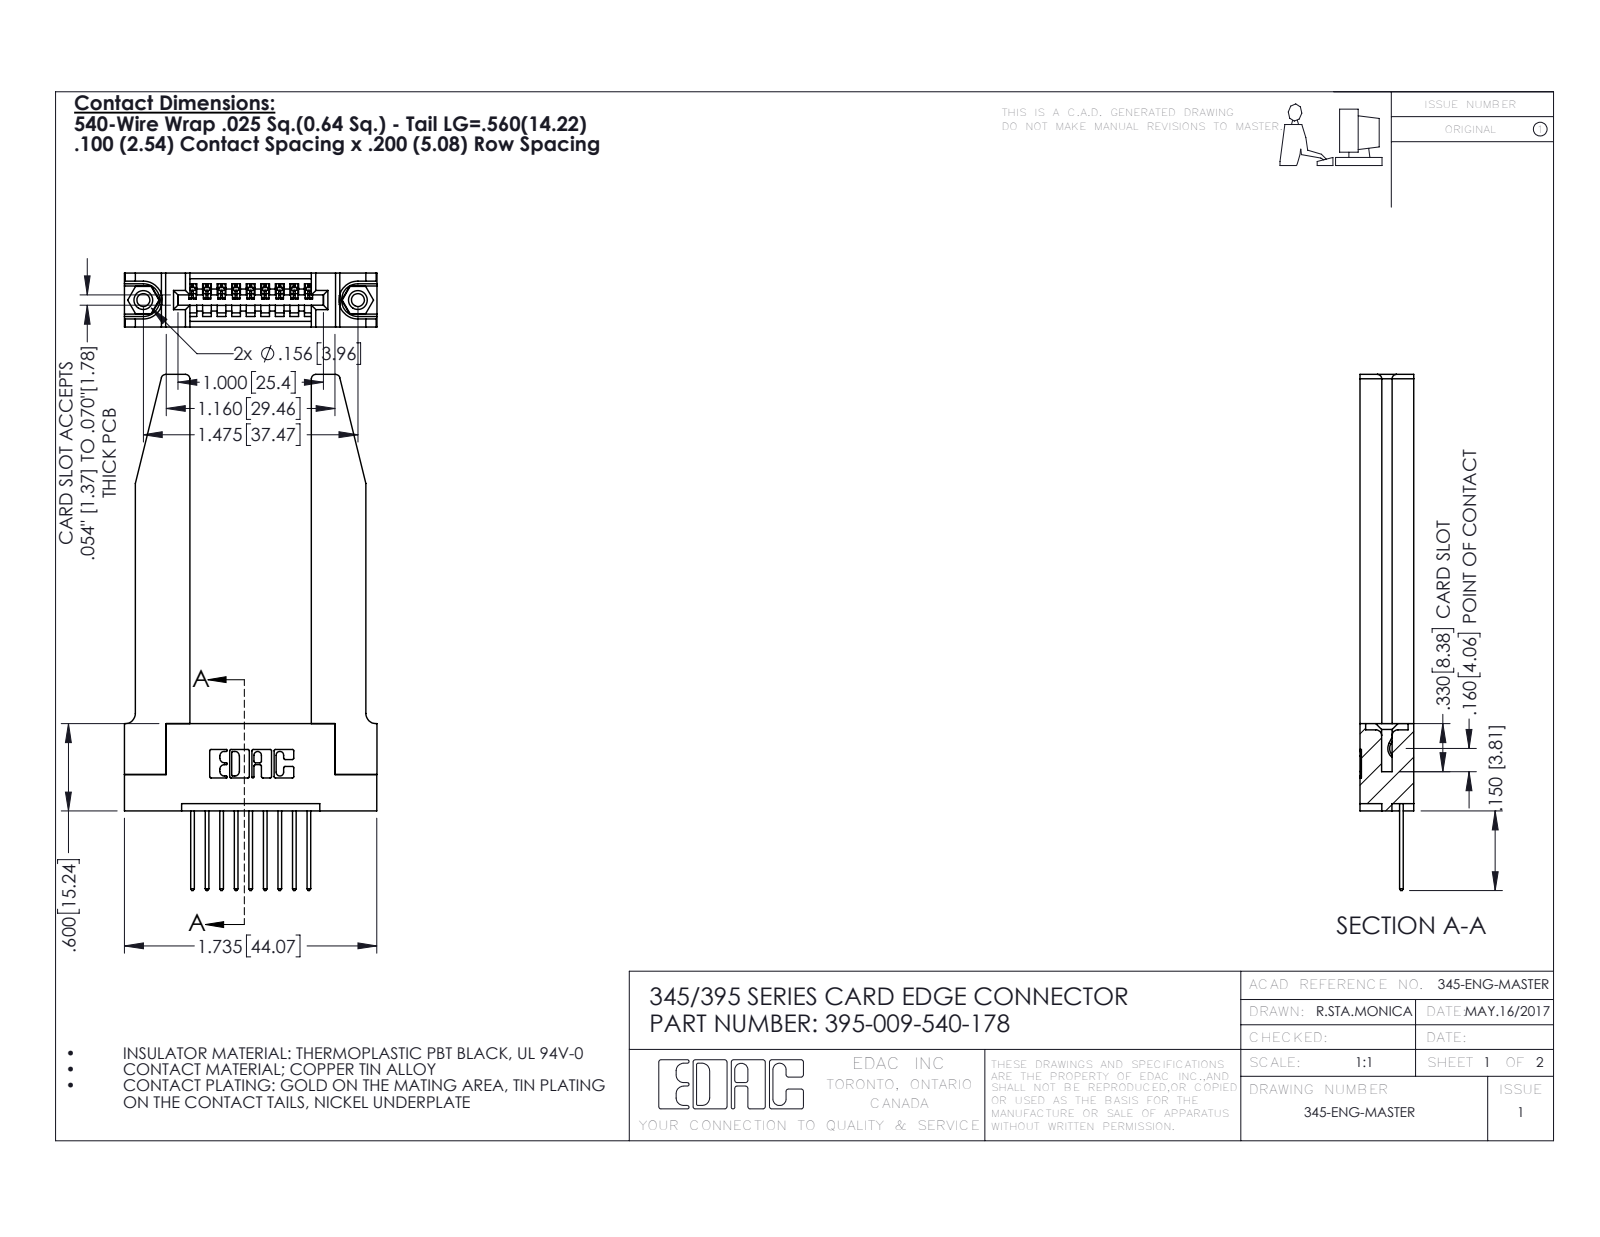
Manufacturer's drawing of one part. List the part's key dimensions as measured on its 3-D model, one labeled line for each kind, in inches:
Part name (STEP PRODUCT): 345-220-078_345-220-078; 395-009-540-178; 345-250-001_345-250-001-102; 345 Part_Flush Mounting Lugs - 0.156 Dia-TH (+1 more)
STEP written by: SolidWorks 2016 (CONFIG_CONTROL_DESIGN)
Units: inches
Bodies: 14 solids, 882 faces (582 planar, 248 cylindrical, 52 other)
Overall size (bounding box): 3.547 × 1.736 × 0.37
Volume: 0.714 in³ · Surface area: 18.15 in²
Round holes (diameter × count): ⌀0.089 ×2, ⌀0.125 ×2, ⌀0.156 ×2, ⌀0.064 ×1
Round bosses / shafts (diameter × count): ⌀0.155 ×2
Partial cylindrical surfaces — rounded edges, fillets, slot ends (radius × count): R0.01 ×22, R0.006 ×18, R0.01 ×18, R0.03 ×8, R0.007 ×6, R0.031 ×6, R0.026 ×3, R0.031 ×2
Main face-to-face distances: 0.37, 0.072, 0.298, 0.15, 0.148, 0.22, 0.2, 0.077, 0.835, 0.098
Hole centre spacings: 0.27, 1.244, 1.475
